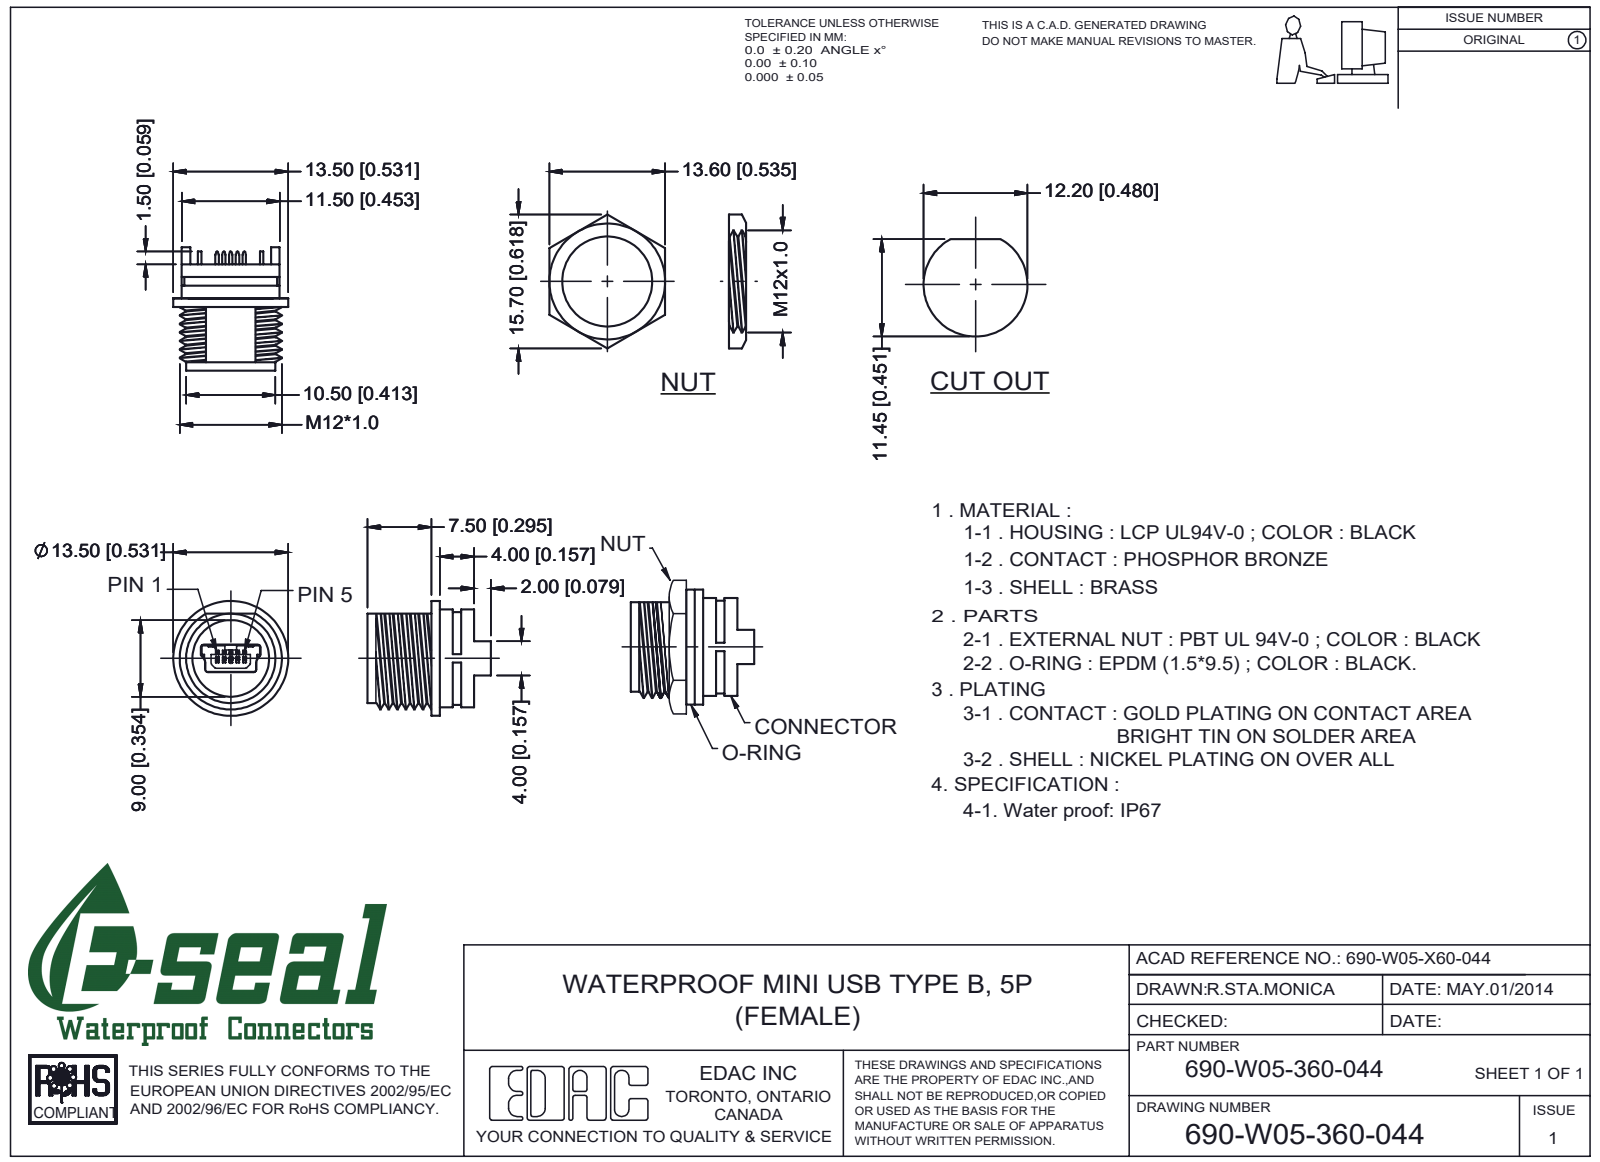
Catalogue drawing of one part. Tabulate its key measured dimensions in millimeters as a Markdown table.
| quantity | value |
| --- | --- |
| part name | 690-W05-360-044 |
| STEP written by | SolidWorks 2020 (AUTOMOTIVE_DESIGN) |
| units | millimeters |
| bodies | 1 solid, 885 faces (593 planar, 235 cylindrical, 57 other) |
| overall size | 15.7 × 14.5 × 14.2 |
| volume | 913 mm³ |
| surface area | 2 247 mm² |
| round holes (diameter × count) | 9 × 1, 9.5 × 1 |
| round bosses / shafts (diameter × count) | 13.5 × 1, 12 × 1, 11.5 × 1, 10.9 × 1, 10.5 × 1 |
| partial cylindrical surfaces (radius × count) | 0.2 × 53, 0.15 × 23, 0.4 × 12, 0.6 × 11, 0.55 × 8, 0.3 × 6, 0.12 × 5, 0.19 × 4 |
| main face-to-face distances | 2.95, 0.4, 3.2, 3.95, 5.45, 3.5, 1.5, 2.25, 0.75, 4 |
